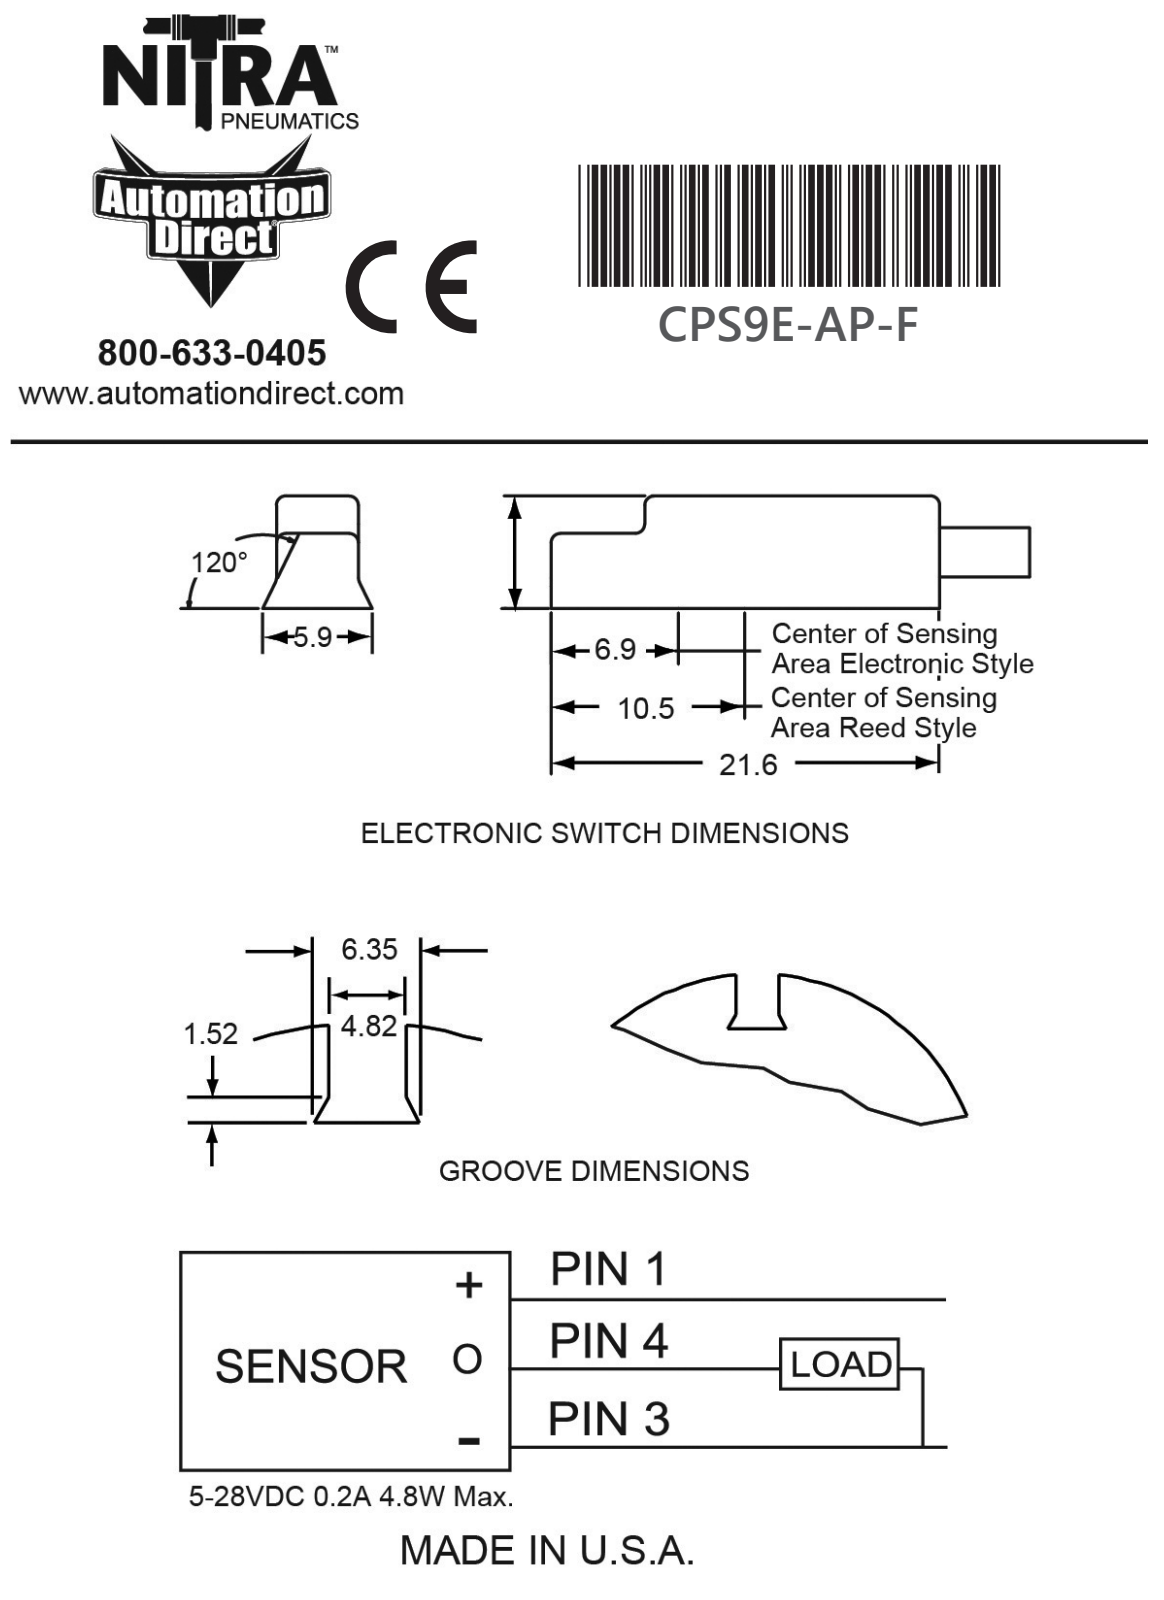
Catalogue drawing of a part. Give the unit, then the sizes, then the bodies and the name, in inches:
Units: inches
Overall size (bounding box): 7.78 × 0.33 × 0.33
Round holes (diameter × count): ⌀0.039 ×3, ⌀0.049 ×3, ⌀0.094 ×1, ⌀0.125 ×1
Round bosses / shafts (diameter × count): ⌀0.044 ×3, ⌀0.039 ×3, ⌀0.33 ×1, ⌀0.31 ×1, ⌀0.309 ×1, ⌀0.3 ×1, ⌀0.276 ×1, ⌀0.256 ×1
Partial cylindrical surfaces — rounded edges, fillets, slot ends (radius × count): R0.02 ×20
Main face-to-face distances: 0.02, 0.1, 0.08, 0.04, 0.06, 0.12, 0.04, 0.06, 0.175, 0.14
Hole centre spacings: 0.097, 0.138, 0.172
Volume: 0.162 in³ · Surface area: 4.79 in²
Bodies: 1 solid, 263 faces (89 planar, 118 cylindrical, 56 other)
Part name (STEP PRODUCT): CPS9E-AP-F
STEP written by: SolidWorks 2023 (CONFIG_CONTROL_DESIGN)
